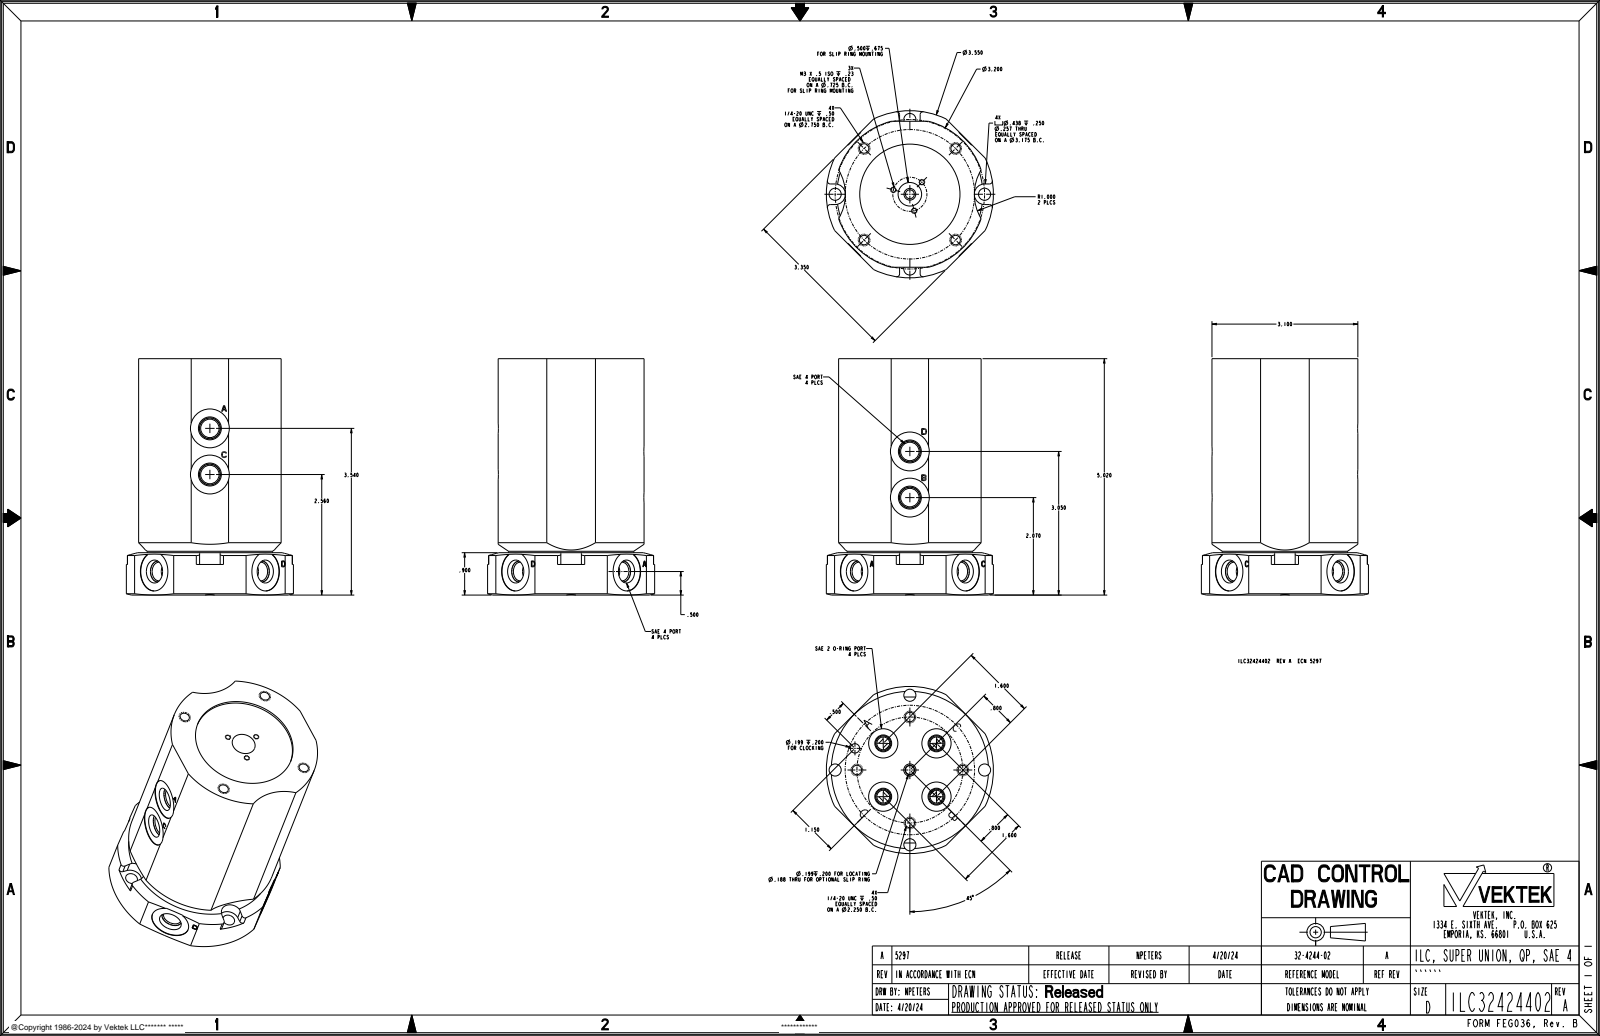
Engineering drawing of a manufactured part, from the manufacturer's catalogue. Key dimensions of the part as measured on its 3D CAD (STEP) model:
Part name (STEP PRODUCT): ILC32424402
STEP written by: CREO PARAMETRIC BY PTC INC, 2021164 (AUTOMOTIVE_DESIGN)
Units: inches
Bodies: 1 solid, 551 faces (275 planar, 168 cylindrical, 108 other)
Overall size (bounding box): 5.02 × 3.35 × 3.35
Volume: 37.96 in³ · Surface area: 100.2 in²
Round holes (diameter × count): ⌀0.25 ×11, ⌀0.201 ×8, ⌀0.392 ×6, ⌀0.825 ×6, ⌀0.257 ×4, ⌀0.272 ×4, ⌀0.621 ×4, ⌀0.098 ×3, ⌀0.118 ×3, ⌀0.199 ×2, ⌀0.188 ×1, ⌀0.5 ×1
Round bosses / shafts (diameter × count): ⌀0.437 ×6, ⌀0.313 ×4, ⌀2.66 ×1
Partial cylindrical surfaces — rounded edges, fillets, slot ends (radius × count): R0.06 ×8, R0.219 ×4, R1 ×2, R1.6 ×1, R1.775 ×1
Main face-to-face distances: 5.02, 4.965, 0.055, 3.099, 0.9, 4.065, 4.12, 3.089, 3.34, 3.35
Hole centre spacings: 0.796, 0.984, 1.15, 1.168, 1.591, 1.783, 1.946, 2.226
